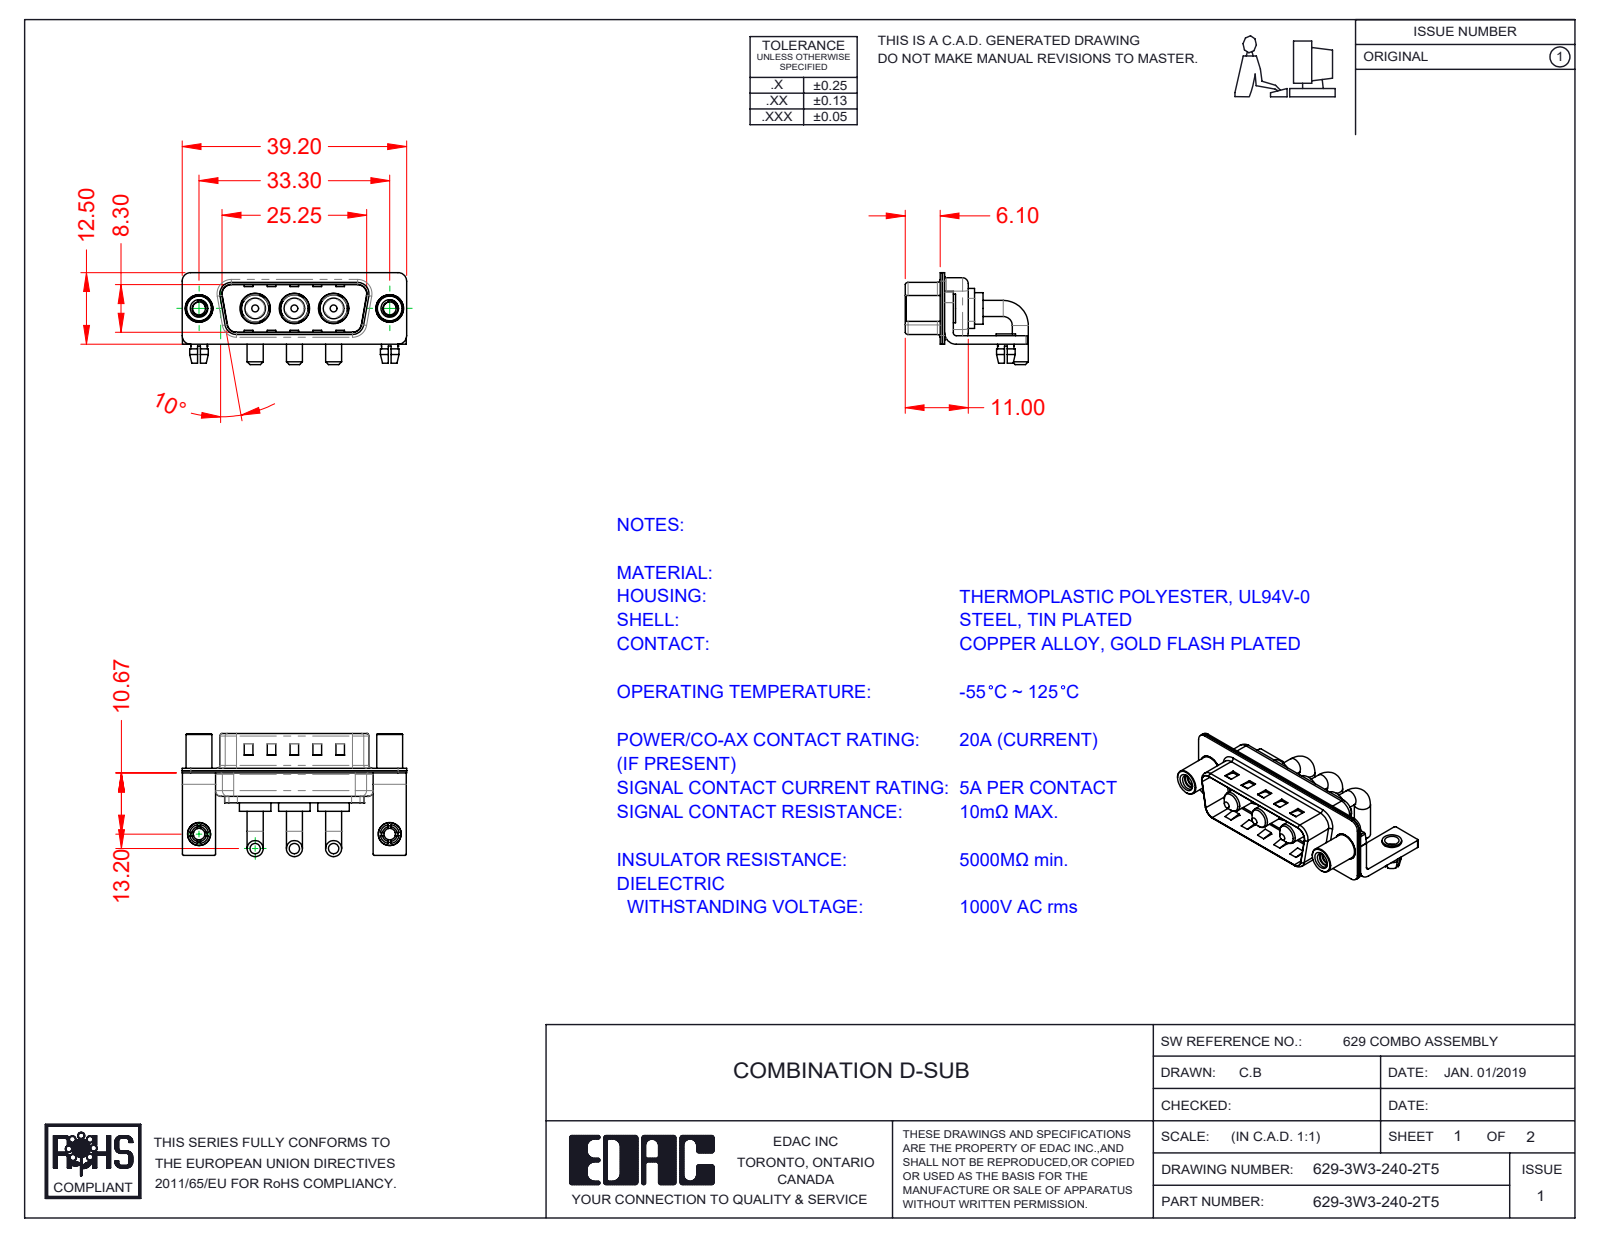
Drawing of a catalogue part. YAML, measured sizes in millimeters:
part_name: "629Combo Shell Rear_15 Contacts; 629Combo Stabilizer Bracket; 629Combo Threaded Standoff_5; 629-3W3-240-2T5 (+4 more)"
step_written_by: "SolidWorks 2020 (CONFIG_CONTROL_DESIGN)"
units: millimeters
bodies: {solids: 15, faces: 649, planar: 239, cylindrical: 288, other: 122}
overall_size: [39.2, 21.5, 16.05]
volume: 2684
surface_area: 6114
round_holes:
  - {diameter: 4.85, count: 3}
  - {diameter: 5.3, count: 3}
  - {diameter: 2, count: 2}
  - {diameter: 2.26, count: 2}
  - {diameter: 2.5, count: 2}
  - {diameter: 3.2, count: 2}
  - {diameter: 4, count: 2}
  - {diameter: 4.8, count: 2}
round_bosses_or_shafts:
  - {diameter: 2.8, count: 6}
  - {diameter: 5.5, count: 3}
  - {diameter: 5.2, count: 3}
  - {diameter: 4.75, count: 3}
  - {diameter: 3.75, count: 3}
  - {diameter: 3.6, count: 3}
  - {diameter: 5, count: 2}
  - {diameter: 4.9, count: 2}
partial_cylinders:
  - {radius: 0.25, count: 16}
  - {radius: 1.5, count: 16}
  - {radius: 2, count: 13}
  - {radius: 0.5, count: 9}
  - {radius: 1.6, count: 8}
  - {radius: 0.6, count: 4}
  - {radius: 0.65, count: 4}
  - {radius: 0.9, count: 4}
face_to_face_distances: [0.4, 0.8, 1.5, 9.5, 8.7, 9.1, 9.9, 5.2, 0.75, 0.6]
hole_center_spacings: [6.85, 9.8, 16.65, 23.5, 33.3, 13.7]
